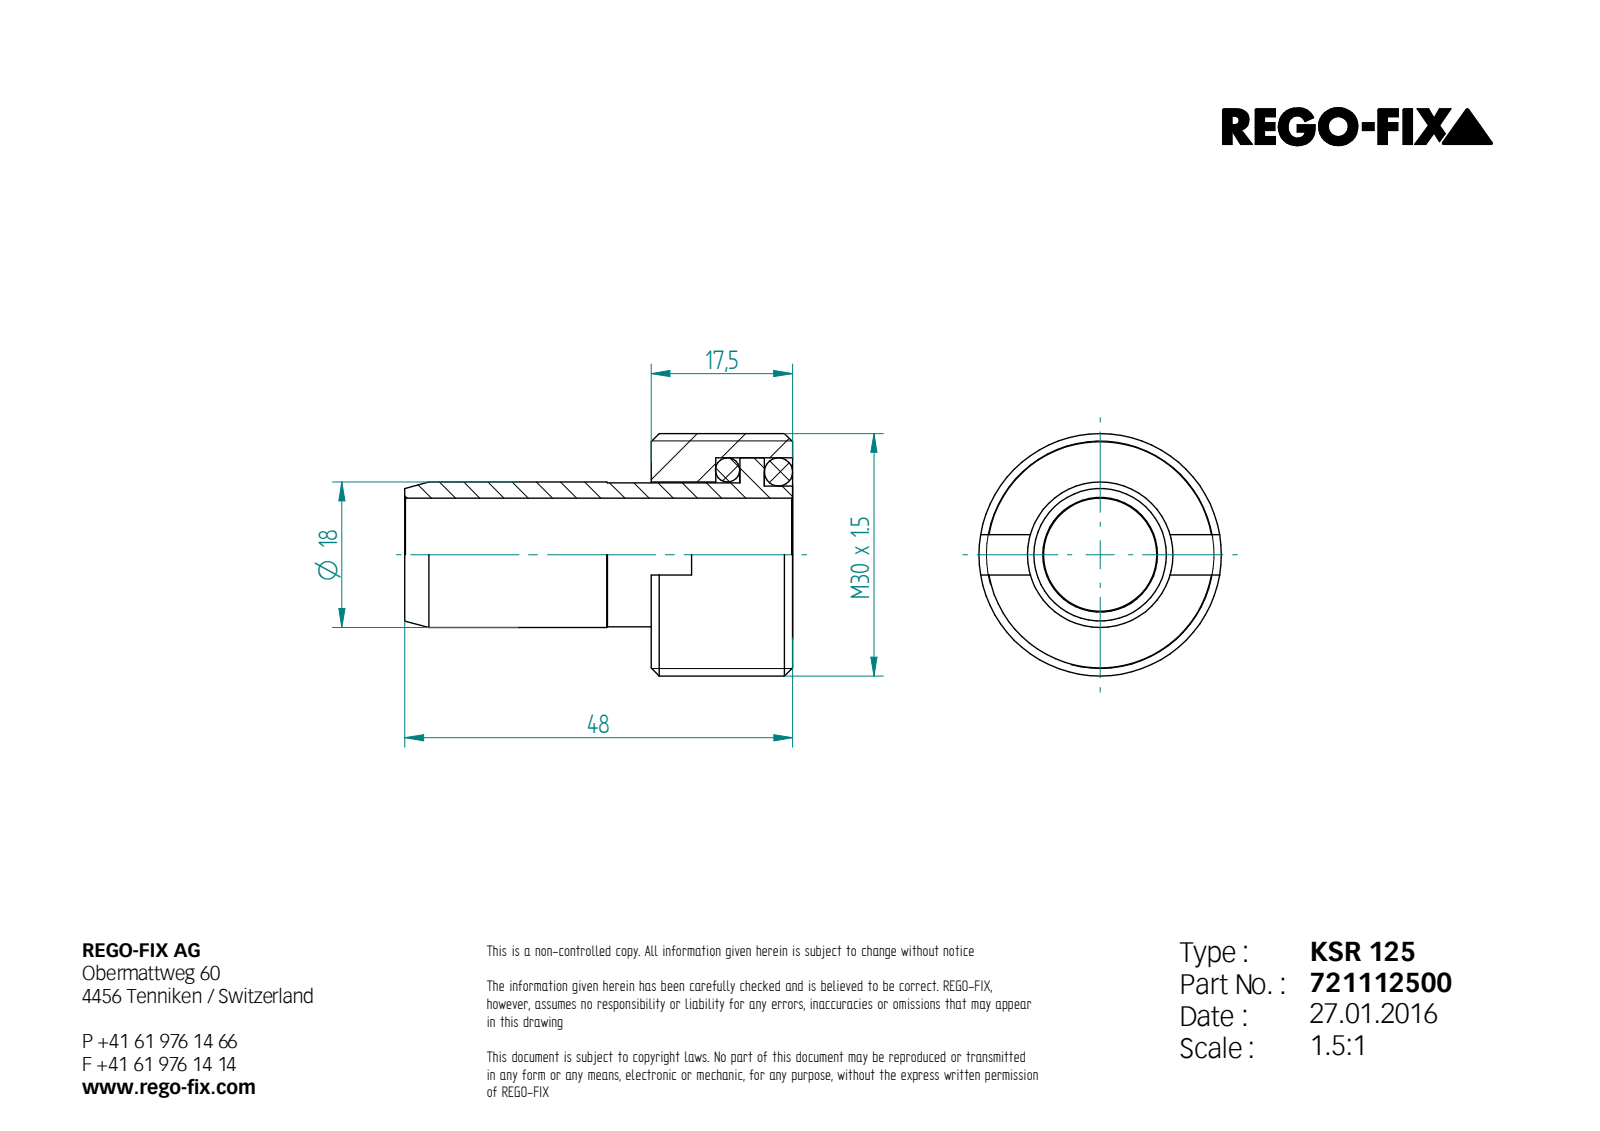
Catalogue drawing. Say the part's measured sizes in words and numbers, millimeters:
The part is named "0012573; 0012574; 0012575; 0012576". Its 3-D file was written by "Unknown (AUTOMOTIVE_DESIGN)". It is 4 solids with 33 faces: 14 planar, 8 cylindrical and 11 other. Overall it measures 48.01 by 30 by 30 millimeters. Its volume is 11 896 cubic millimeters and its surface area 10 372 square millimeters. Round holes: 1 of diameter 14, 1 of diameter 18, 1 of diameter 24. Round bosses or shafts: 1 of diameter 30, 1 of diameter 17.8, 1 of diameter 17. The main face-to-face distances are 3, 6, 17.5, 14, 3.5, 8, 9.5, 11, 6.5, 5.
